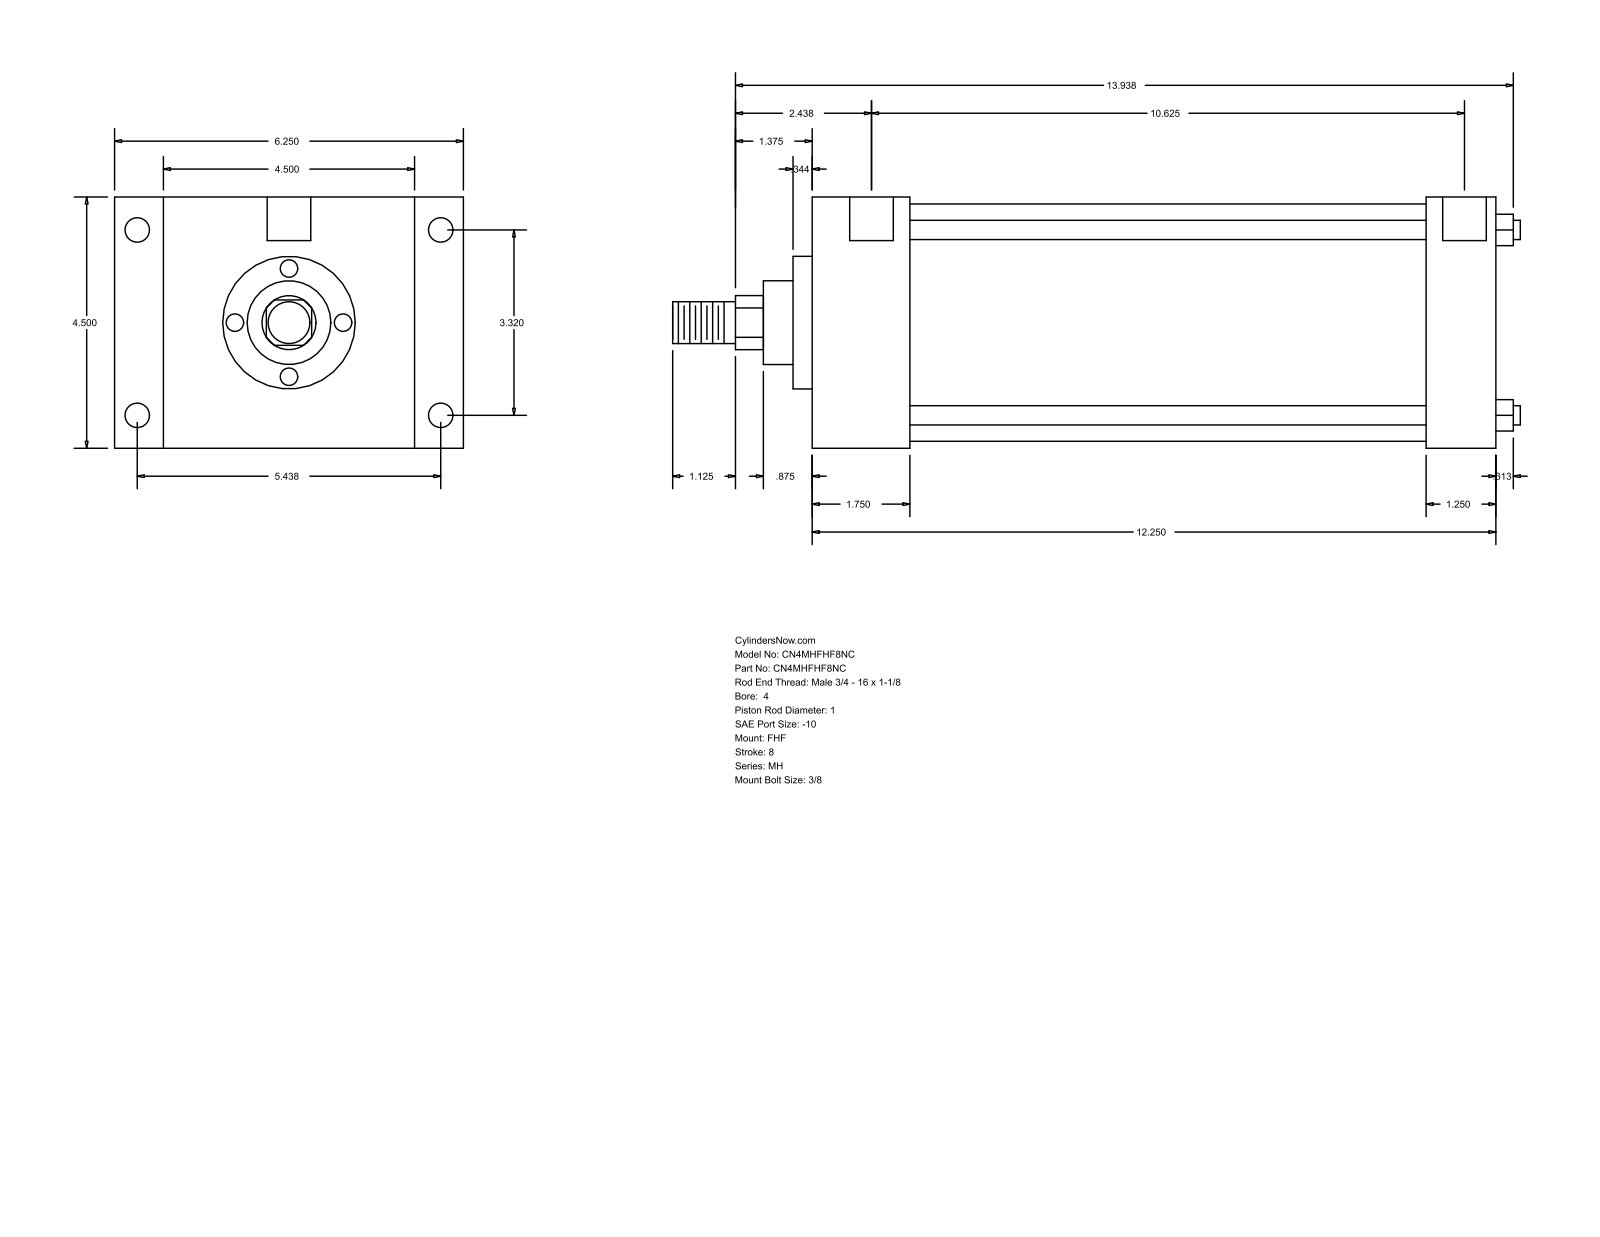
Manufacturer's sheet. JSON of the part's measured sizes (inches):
{"part_name": "MH_FHF__0400_1", "step_written_by": "GSSL Pune (CONFIG_CONTROL_DESIGN)", "units": "inches", "bodies": {"solids": 0, "faces": 90, "planar": 61, "cylindrical": 29, "other": 0}, "overall_size": [15.187, 6.25, 4.5], "round_holes": [[0.344, 4], [0.438, 4], [0.781, 2]], "round_bosses_or_shafts": [[0.345, 4], [4.25, 1], [2.375, 1], [1.5, 1], [1, 1], [0.75, 1]], "partial_cylinders_radius": [[0.484, 1]], "face_to_face_distances": [4.5, 12.25, 1.75, 10.5, 0.875, 5.375, 6.25, 11, 9.25, 1.25], "hole_center_spacings": [3.32, 5.438, 6.371, 10.75, 0.062, 0.063, 10.625, 10.687]}
